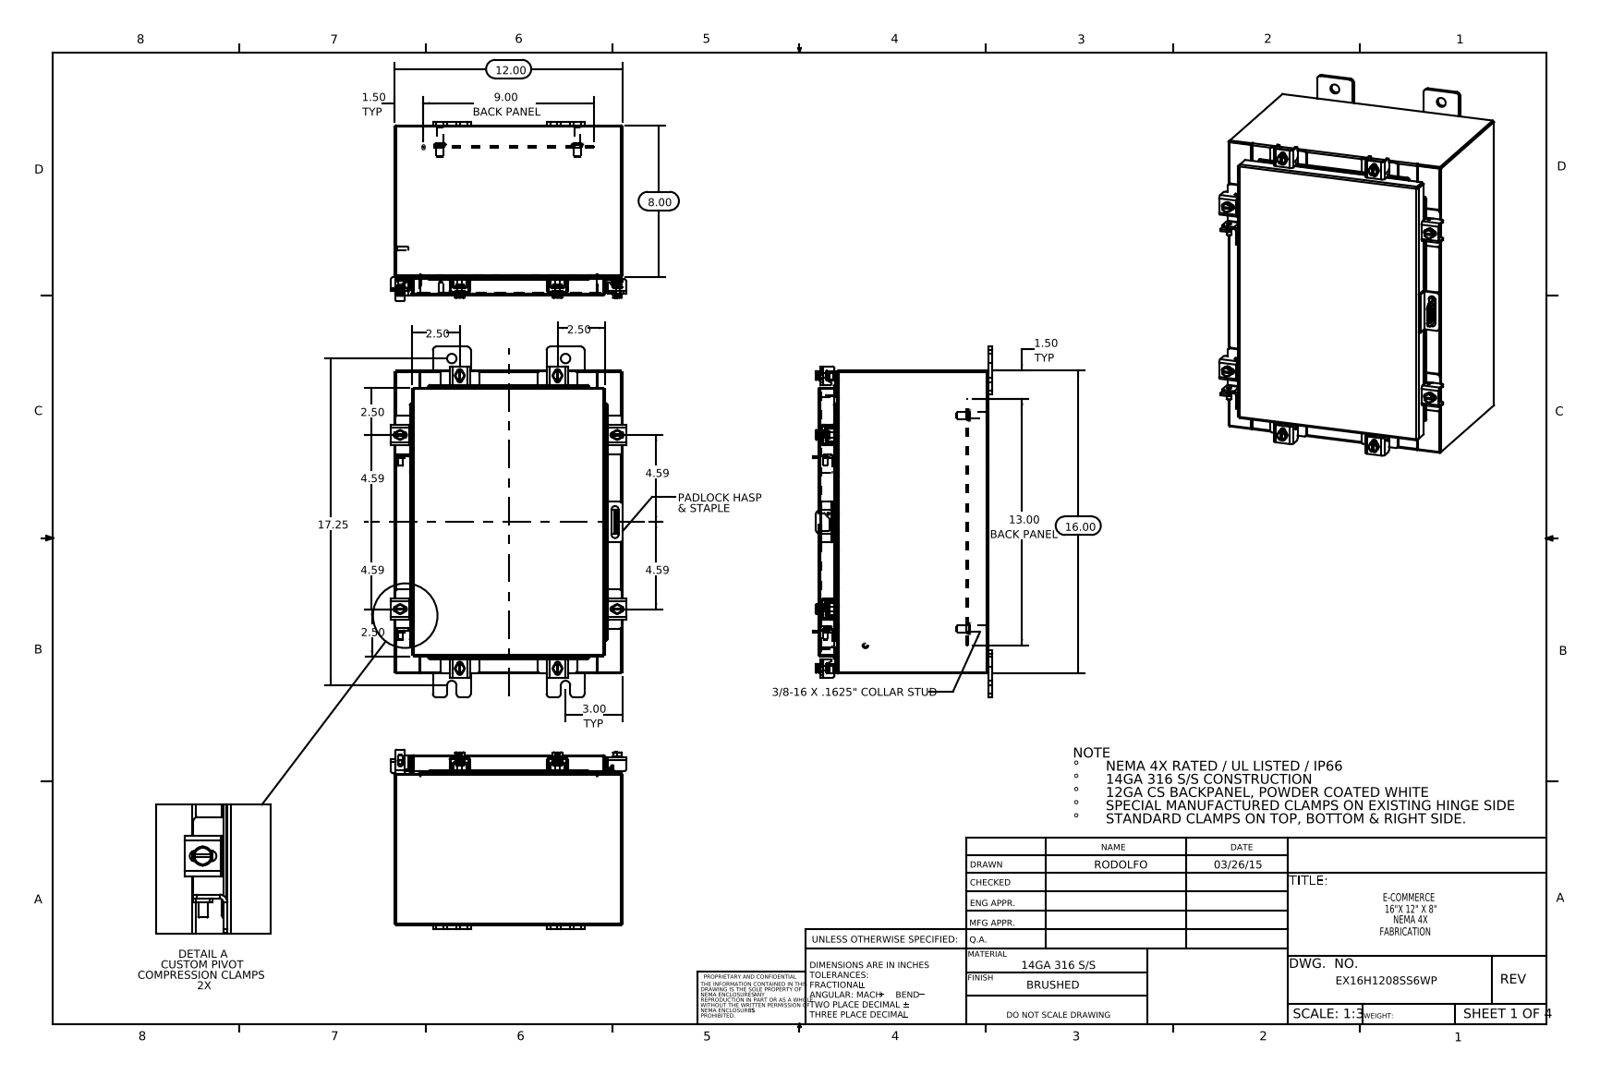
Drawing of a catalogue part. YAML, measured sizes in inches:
part_name: "EX16H1208SS6WP; 30X10 Clamp Bracket2; N-WMT04X30402202210-00 Clamp Top; N-WMT04X30402202210-00 22101002 (+8 more)"
step_written_by: "SolidWorks 2014 (CONFIG_CONTROL_DESIGN)"
units: inches
bodies: {solids: 61, faces: 1534, planar: 823, cylindrical: 583, other: 128}
overall_size: [18.5, 12.421, 9.453]
volume: 90.11
surface_area: 2285
round_holes:
  - {diameter: 0.213, count: 8}
  - {diameter: 0.26, count: 8}
  - {diameter: 0.5, count: 8}
  - {diameter: 0.125, count: 1}
  - {diameter: 0.25, count: 1}
round_bosses_or_shafts:
  - {diameter: 0.5, count: 8}
  - {diameter: 0.25, count: 8}
  - {diameter: 0.399, count: 6}
  - {diameter: 0.625, count: 4}
  - {diameter: 0.375, count: 4}
  - {diameter: 0.33, count: 4}
  - {diameter: 0.315, count: 2}
  - {diameter: 0.236, count: 2}
partial_cylinders:
  - {radius: 0.06, count: 36}
  - {radius: 0.19, count: 24}
  - {radius: 0.013, count: 22}
  - {radius: 0.088, count: 22}
  - {radius: 0.1, count: 16}
  - {radius: 0.141, count: 16}
  - {radius: 0.09, count: 14}
  - {radius: 0.12, count: 14}
face_to_face_distances: [0.075, 8.9, 11.925, 15.925, 8.975, 8.826, 7.925, 0.975, 11.85, 1]
hole_center_spacings: [2.347, 4.44, 8.874, 10.433, 12.715, 13.392, 13.852, 14.857]
